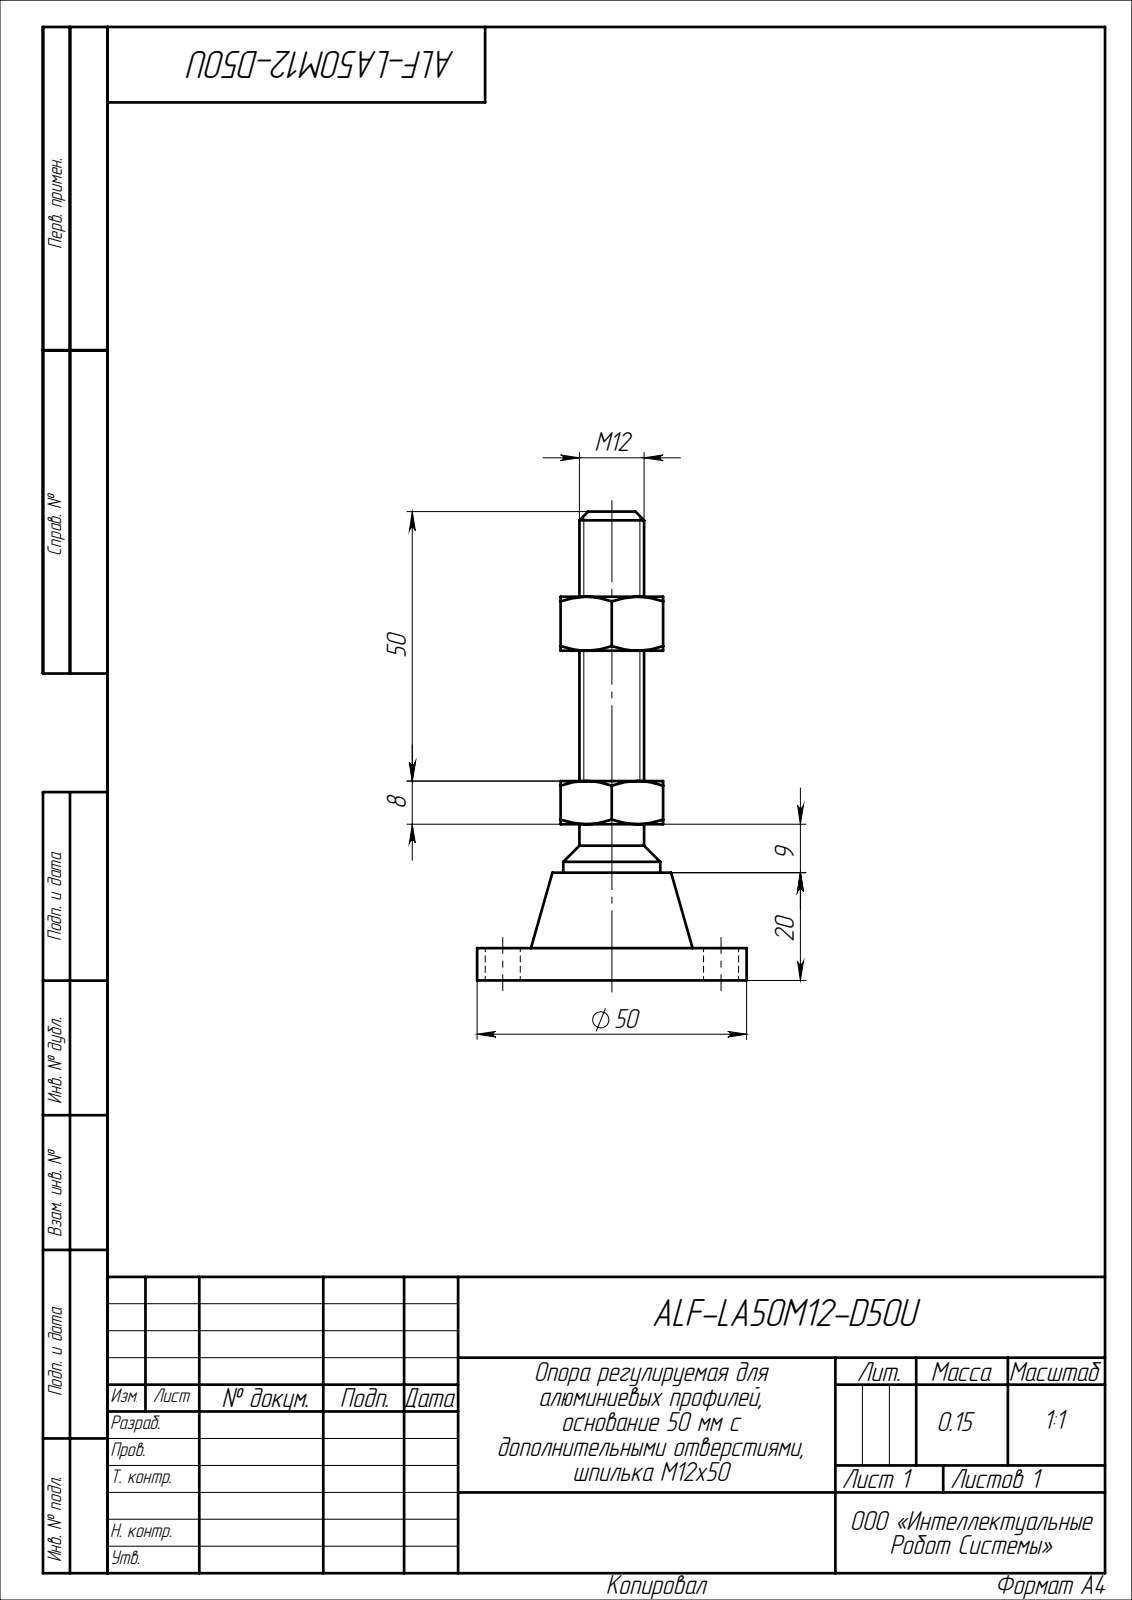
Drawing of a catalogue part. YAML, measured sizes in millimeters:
part_name: "ALF-LA50M12-D50U"
step_written_by: "SolidWorks 2022 (CONFIG_CONTROL_DESIGN)"
units: millimeters
bodies: {solids: 1, faces: 64, planar: 20, cylindrical: 14, other: 30}
overall_size: [87, 50, 50]
volume: 30451
surface_area: 9560
round_holes:
  - {diameter: 6.5, count: 2}
round_bosses_or_shafts:
  - {diameter: 50, count: 1}
  - {diameter: 18, count: 1}
  - {diameter: 12, count: 1}
face_to_face_distances: [6, 19, 37, 31, 61.2, 55.2, 24.2, 29, 23, 8]
hole_center_spacings: [40.5]
